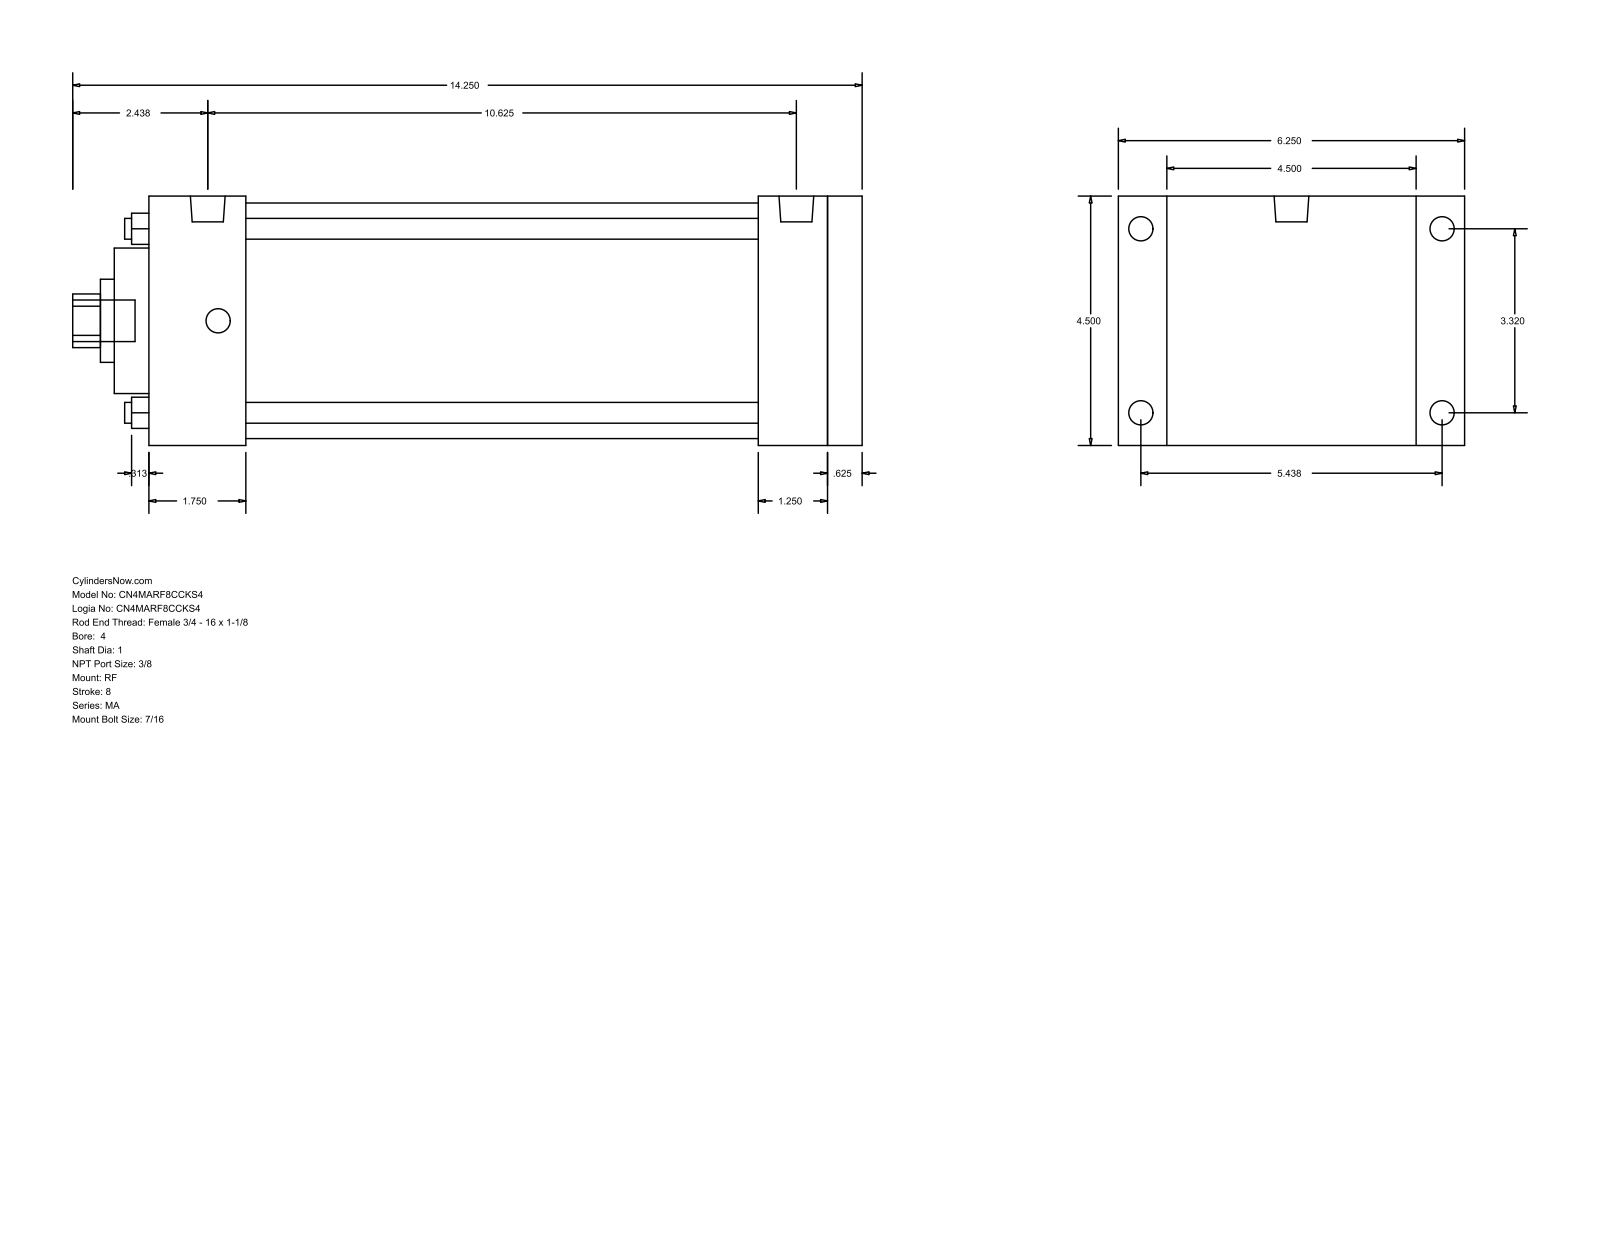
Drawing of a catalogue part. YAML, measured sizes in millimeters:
part_name: "MA_RF__0400_1"
step_written_by: "GSSL Pune (CONFIG_CONTROL_DESIGN)"
units: millimeters
bodies: {solids: 0, faces: 94, planar: 65, cylindrical: 29, other: 0}
overall_size: [361.95, 158.75, 114.3]
round_holes:
  - {diameter: 9.53, count: 4}
  - {diameter: 25.4, count: 1}
  - {diameter: 38.1, count: 1}
  - {diameter: 66.67, count: 1}
  - {diameter: 107.95, count: 1}
round_bosses_or_shafts:
  - {diameter: 11.11, count: 8}
  - {diameter: 15.93, count: 2}
  - {diameter: 19.05, count: 1}
partial_cylinders:
  - {radius: 12.29, count: 1}
face_to_face_distances: [114.3, 327.03, 311.15, 15.88, 22.23, 136.53, 279.4, 31.75, 47.63, 44.46]
hole_center_spacings: [59.62, 84.32, 119.25]
